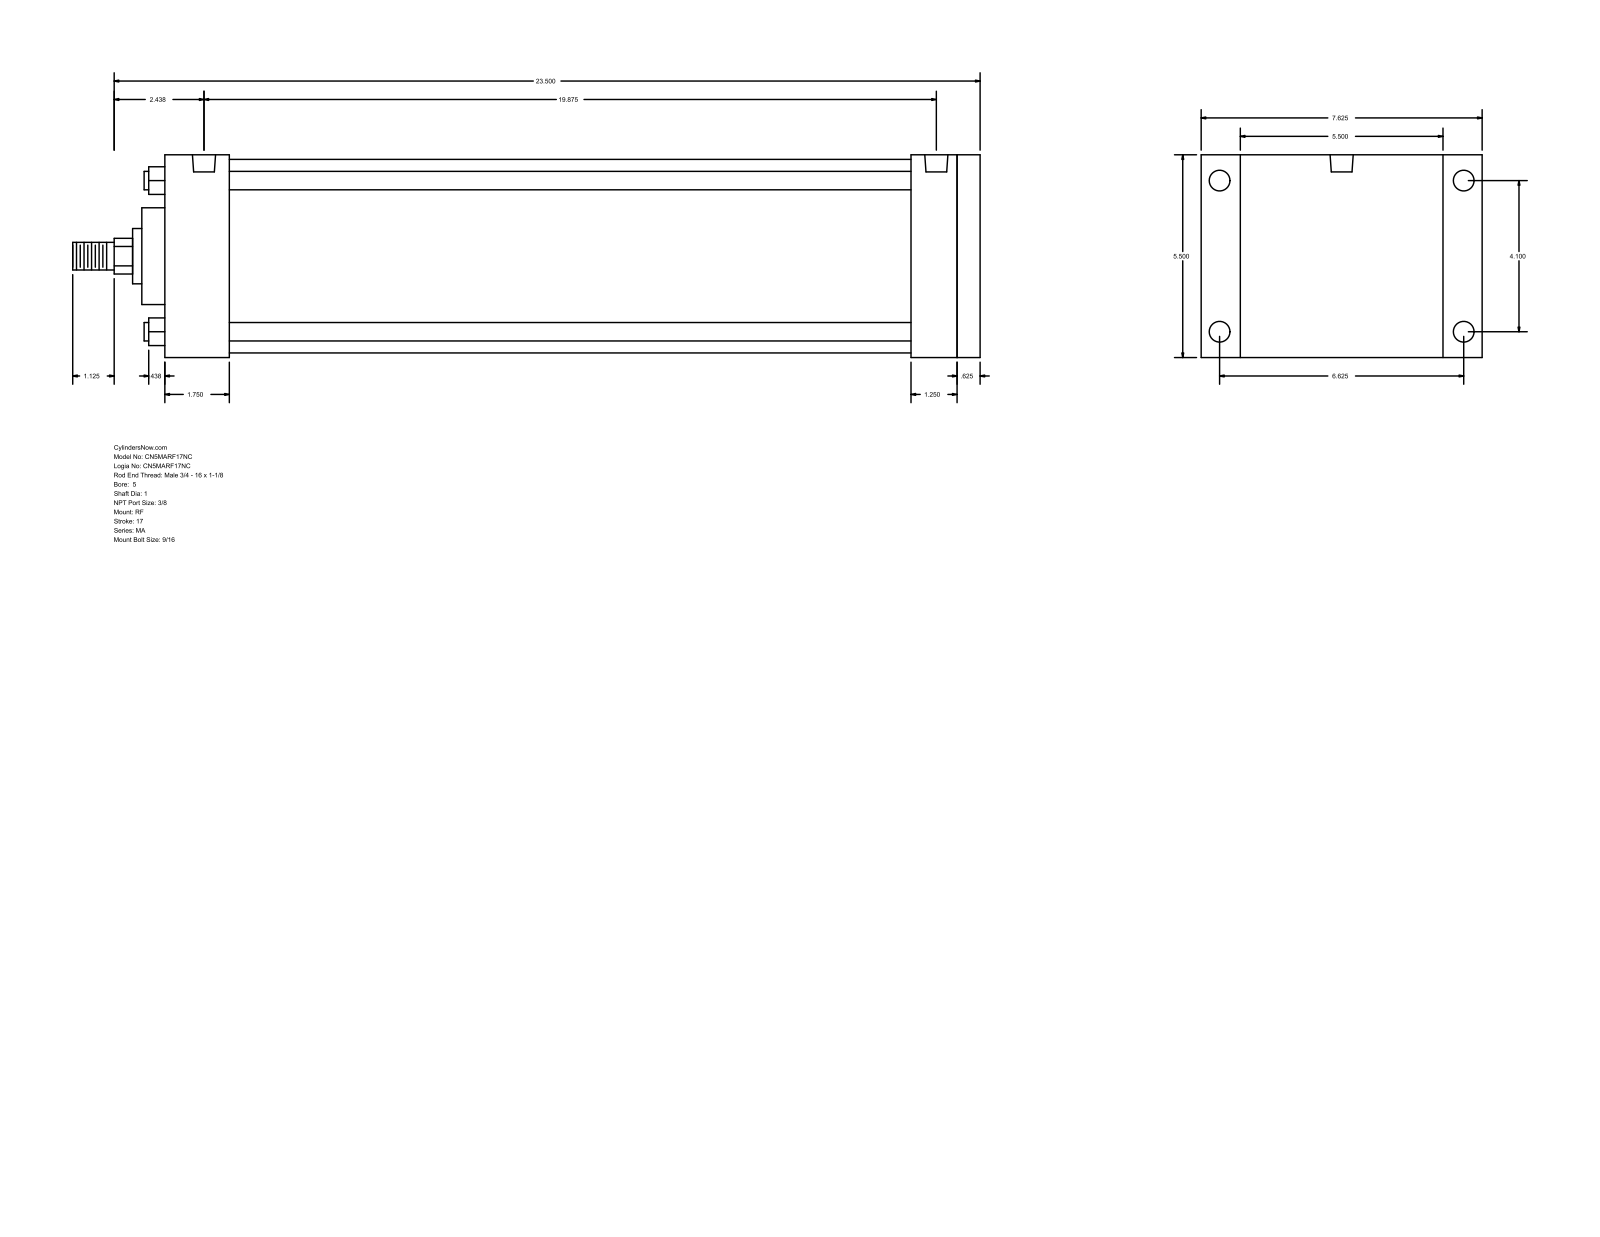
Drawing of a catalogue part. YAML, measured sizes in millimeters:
part_name: "MA_RF__0500_1"
step_written_by: "GSSL Pune (CONFIG_CONTROL_DESIGN)"
units: millimeters
bodies: {solids: 0, faces: 94, planar: 65, cylindrical: 29, other: 0}
overall_size: [625.48, 193.68, 139.7]
round_holes:
  - {diameter: 11.11, count: 4}
  - {diameter: 14.29, count: 4}
  - {diameter: 15.93, count: 2}
round_bosses_or_shafts:
  - {diameter: 12.7, count: 4}
  - {diameter: 133.35, count: 1}
  - {diameter: 66.67, count: 1}
  - {diameter: 38.1, count: 1}
  - {diameter: 25.4, count: 1}
  - {diameter: 19.05, count: 1}
partial_cylinders:
  - {radius: 12.29, count: 1}
face_to_face_distances: [139.7, 561.98, 546.1, 15.88, 44.46, 501.64, 517.52, 514.35, 469.89, 31.75]
hole_center_spacings: [4.76, 104.14, 168.28, 197.9, 495.31, 500.07, 504.83]
